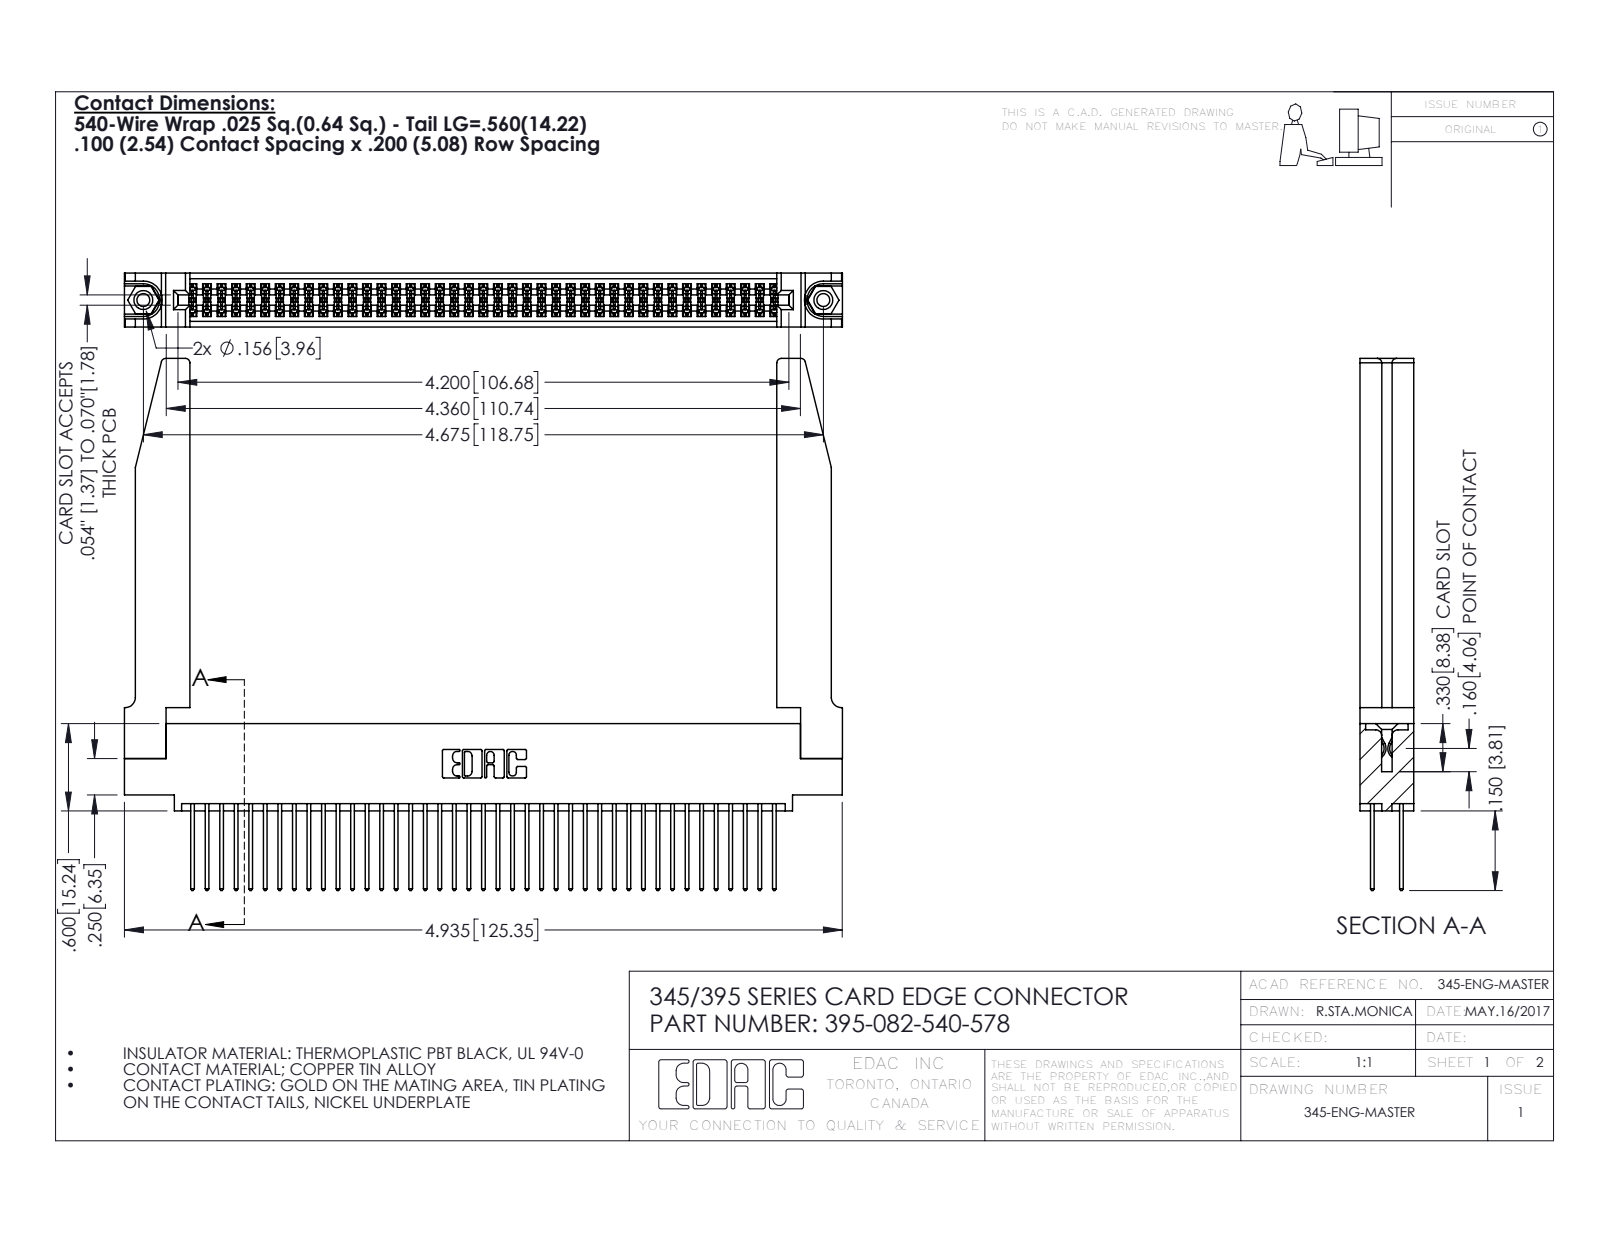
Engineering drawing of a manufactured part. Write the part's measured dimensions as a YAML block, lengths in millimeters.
part_name: "345-250-001_345-250-001-102; 345-292-001_345-293-140; 345-220-078_345-220-078; 345 Part_0.110 Offset - 0.156 Dia-TH (+1 more)"
step_written_by: "SolidWorks 2016 (CONFIG_CONTROL_DESIGN)"
units: millimeters
bodies: {solids: 87, faces: 4464, planar: 2932, cylindrical: 1480, other: 52}
overall_size: [125.4, 92.9, 9.4]
volume: 20170
surface_area: 26700
round_holes:
  - {diameter: 2.3, count: 2}
  - {diameter: 3.2, count: 2}
  - {diameter: 4, count: 2}
  - {diameter: 1.6, count: 1}
round_bosses_or_shafts:
  - {diameter: 3.9, count: 2}
partial_cylinders:
  - {radius: 0.2, count: 123}
  - {radius: 0.3, count: 82}
  - {radius: 0.3, count: 22}
  - {radius: 0.8, count: 8}
  - {radius: 0.2, count: 6}
  - {radius: 0.8, count: 6}
  - {radius: 0.7, count: 3}
  - {radius: 0.4, count: 2}
face_to_face_distances: [1.8, 7.6, 9.4, 5.1, 2.5, 6.9, 0.6, 5.7, 4.4, 3.8]
hole_center_spacings: [6.9, 112.8, 118.7]
